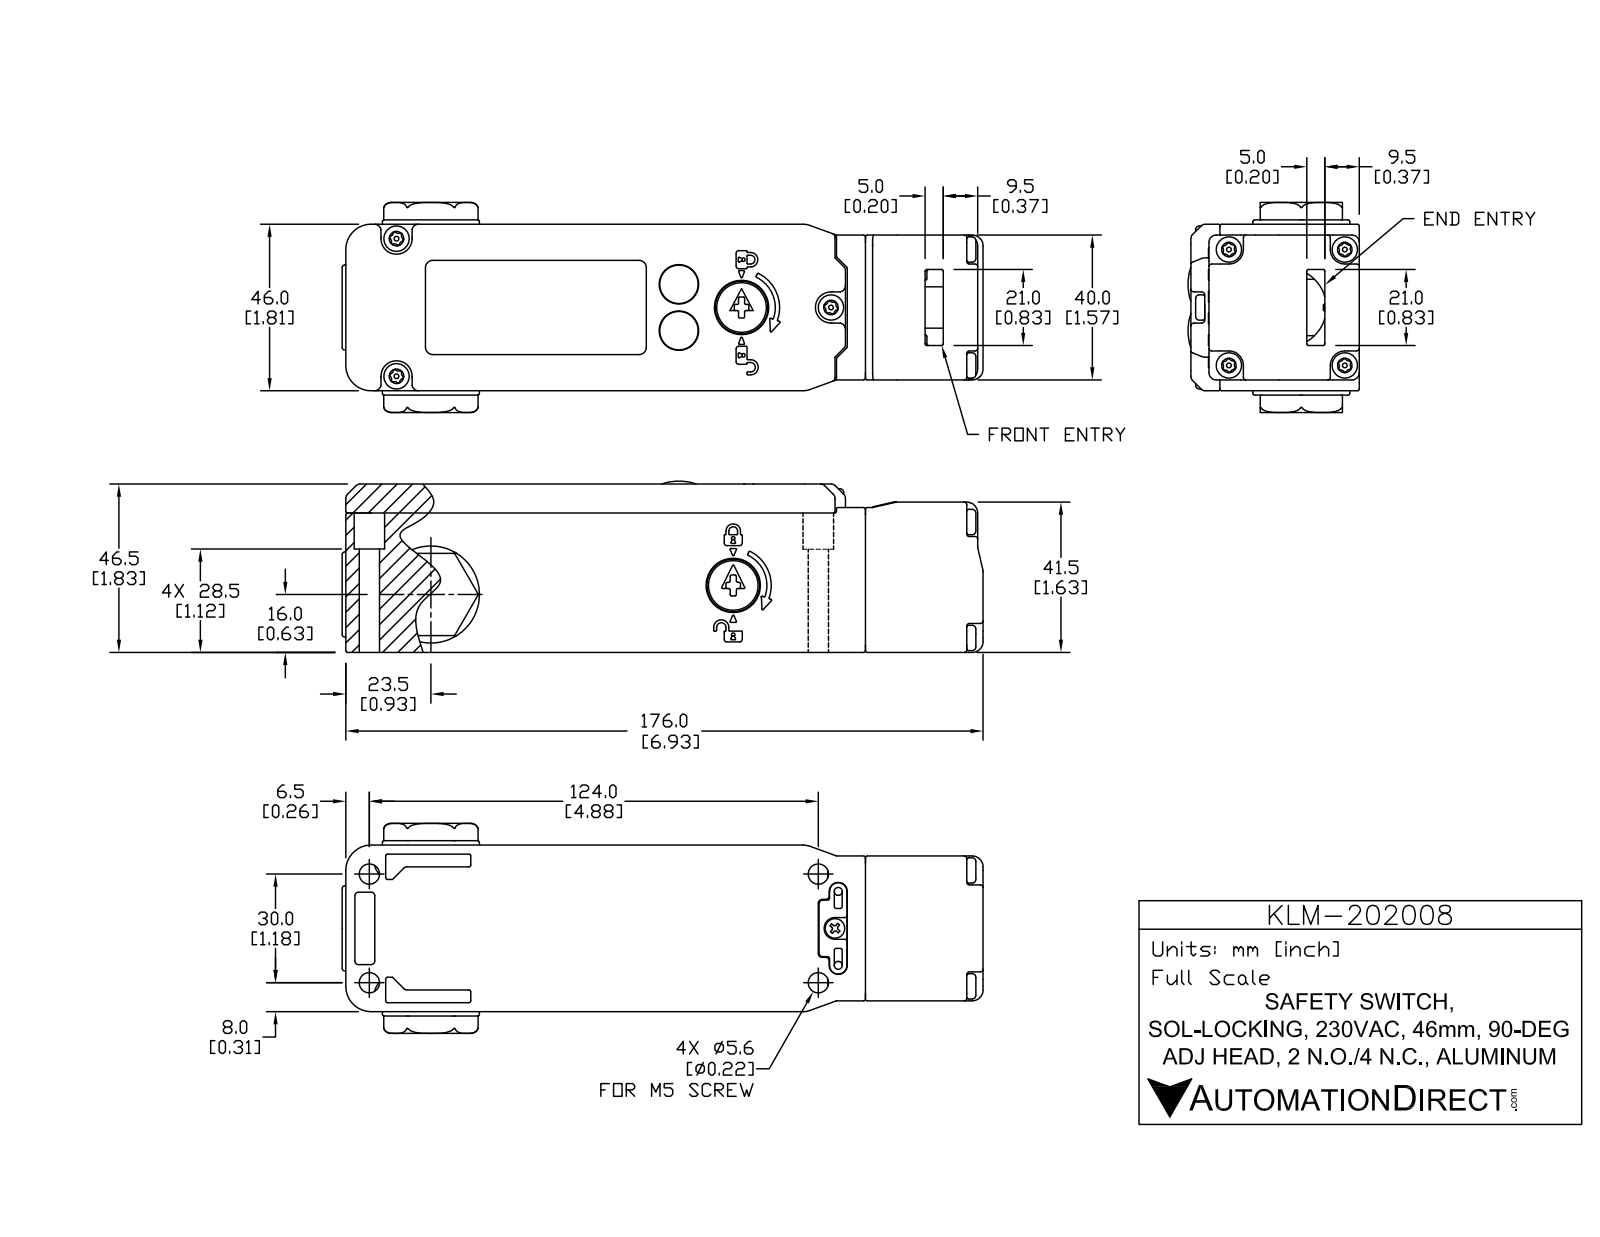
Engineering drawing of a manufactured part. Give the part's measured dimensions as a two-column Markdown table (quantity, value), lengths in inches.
| quantity | value |
| --- | --- |
| part name | KLM-202008 |
| STEP written by | SolidWorks 2017 (AUTOMOTIVE_DESIGN) |
| units | inches |
| bodies | 19 solids, 4517 faces (1071 planar, 1803 cylindrical, 1643 other) |
| overall size | 6.969 × 2.283 × 1.861 |
| volume | 7.308 in³ |
| surface area | 146.4 in² |
| round holes (diameter × count) | 0.157 × 7, 0.118 × 6, 0.169 × 4, 0.197 × 4, 0.22 × 4, 0.362 × 4, 0.146 × 3, 0.165 × 3, 0.177 × 3, 0.315 × 3, 0.079 × 2, 0.087 × 2 |
| round bosses / shafts (diameter × count) | 0.276 × 7, 0.138 × 7, 0.051 × 7, 0.039 × 4, 0.236 × 3, 0.571 × 2, 0.449 × 2, 0.417 × 2 |
| partial cylindrical surfaces (radius × count) | 0.02 × 519, 0.008 × 139, 0.012 × 115, 0.039 × 111, 0.016 × 70, 0.028 × 42, 0.031 × 36, 0.059 × 25 |
| main face-to-face distances | 0.091, 1.72, 0.087, 1.811, 0.028, 0.098, 1.602, 0.118, 1.732, 1.646 |
| hole center spacings | 0.891, 1.26, 0.139, 0.276, 0.277, 0.287, 0.329, 0.335 |
